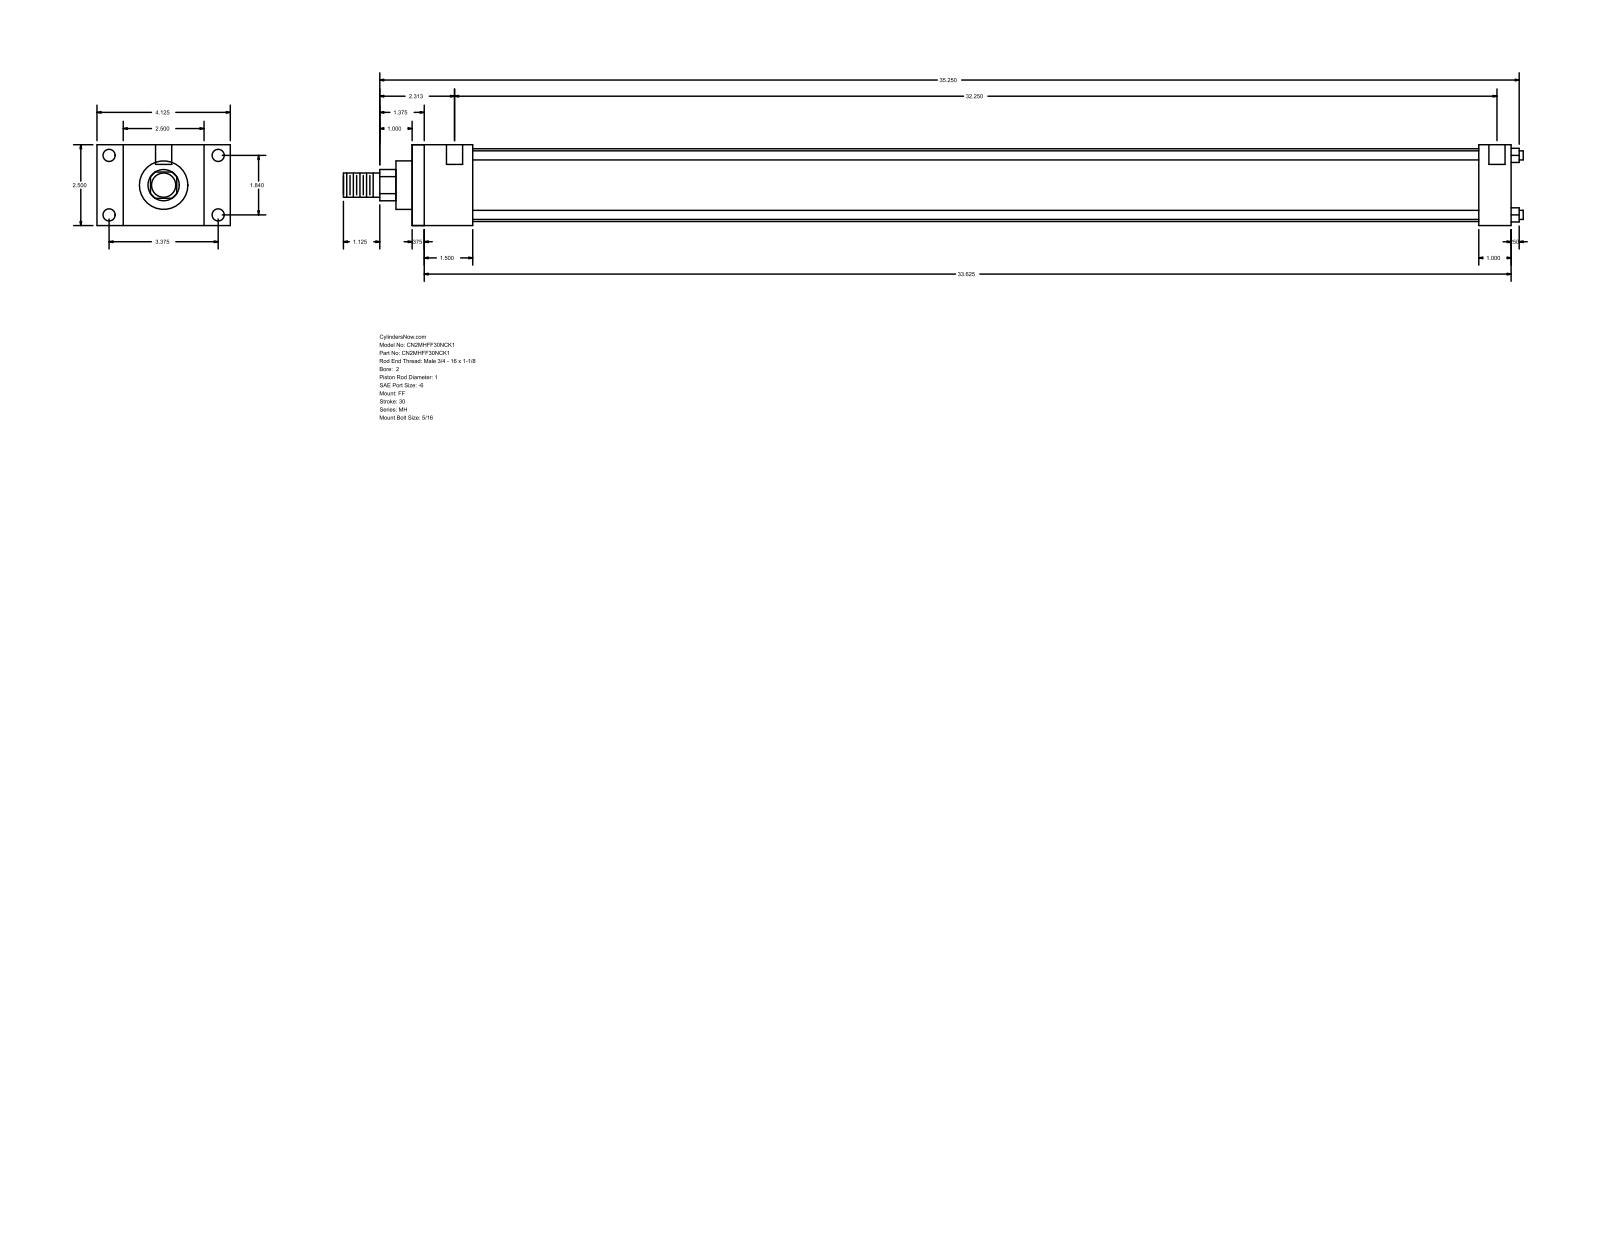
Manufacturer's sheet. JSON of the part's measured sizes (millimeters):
{"part_name": "MH_FF__0200_1", "step_written_by": "GSSL Pune (CONFIG_CONTROL_DESIGN)", "units": "millimeters", "bodies": {"solids": 0, "faces": 92, "planar": 64, "cylindrical": 28, "other": 0}, "overall_size": [927.1, 104.78, 63.5], "round_holes": [[5.56, 4], [9.53, 4], [12.7, 2]], "round_bosses_or_shafts": [[7.14, 4], [57.15, 1], [38.1, 1], [25.4, 1], [19.05, 1]], "partial_cylinders_radius": [[12.29, 1]], "face_to_face_distances": [63.5, 863.6, 9.52, 854.08, 20.64, 25.4, 47.63, 838.2, 38.11, 828.68], "hole_center_spacings": [46.74, 85.72, 97.63, 827.08, 3.17, 4.76, 819.15, 822.32]}
